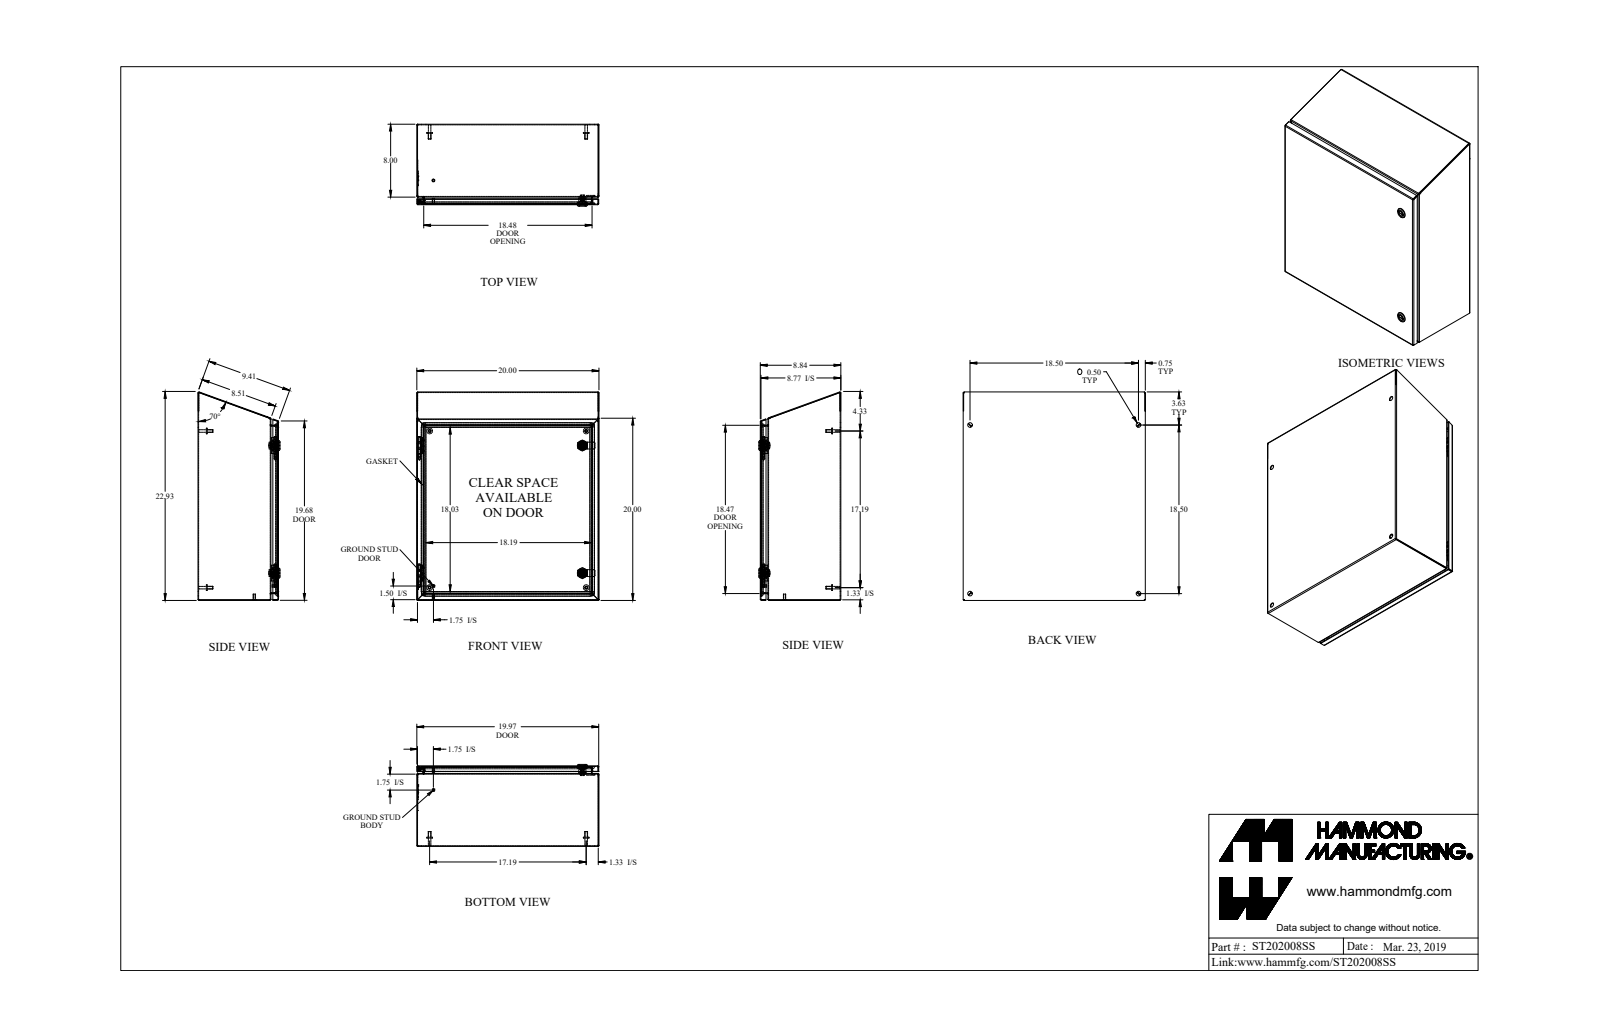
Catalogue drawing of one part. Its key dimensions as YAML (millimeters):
part_name: "ST202008SS"
step_written_by: "SolidWorks 2018 (AUTOMOTIVE_DESIGN)"
units: millimeters
bodies: {solids: 27, faces: 777, planar: 410, cylindrical: 231, other: 136}
overall_size: [581.2, 508, 228.5]
volume: 2114000
surface_area: 2292000
round_holes:
  - {diameter: 12.7, count: 6}
  - {diameter: 5, count: 2}
  - {diameter: 9.8, count: 2}
  - {diameter: 16, count: 2}
  - {diameter: 19.5, count: 2}
  - {diameter: 4.4, count: 1}
  - {diameter: 6.1, count: 1}
  - {diameter: 6.1, count: 1}
round_bosses_or_shafts:
  - {diameter: 8, count: 6}
  - {diameter: 15.9, count: 4}
  - {diameter: 7, count: 4}
  - {diameter: 27.9, count: 2}
  - {diameter: 19.9, count: 2}
  - {diameter: 15.9, count: 2}
  - {diameter: 13.3, count: 2}
  - {diameter: 6.4, count: 2}
partial_cylinders:
  - {radius: 0.9, count: 20}
  - {radius: 2.7, count: 20}
  - {radius: 6.4, count: 11}
  - {radius: 0.2, count: 4}
  - {radius: 1.6, count: 4}
  - {radius: 3.2, count: 4}
  - {radius: 12.7, count: 4}
  - {radius: 7.8, count: 2}
face_to_face_distances: [1.8, 222.6, 220.8, 224.5, 506.2, 504.3, 508, 201.4, 21.3, 23.1]
hole_center_spacings: [469.9, 63.3, 413.6, 446.3, 605.2, 664.5, 355.6]
